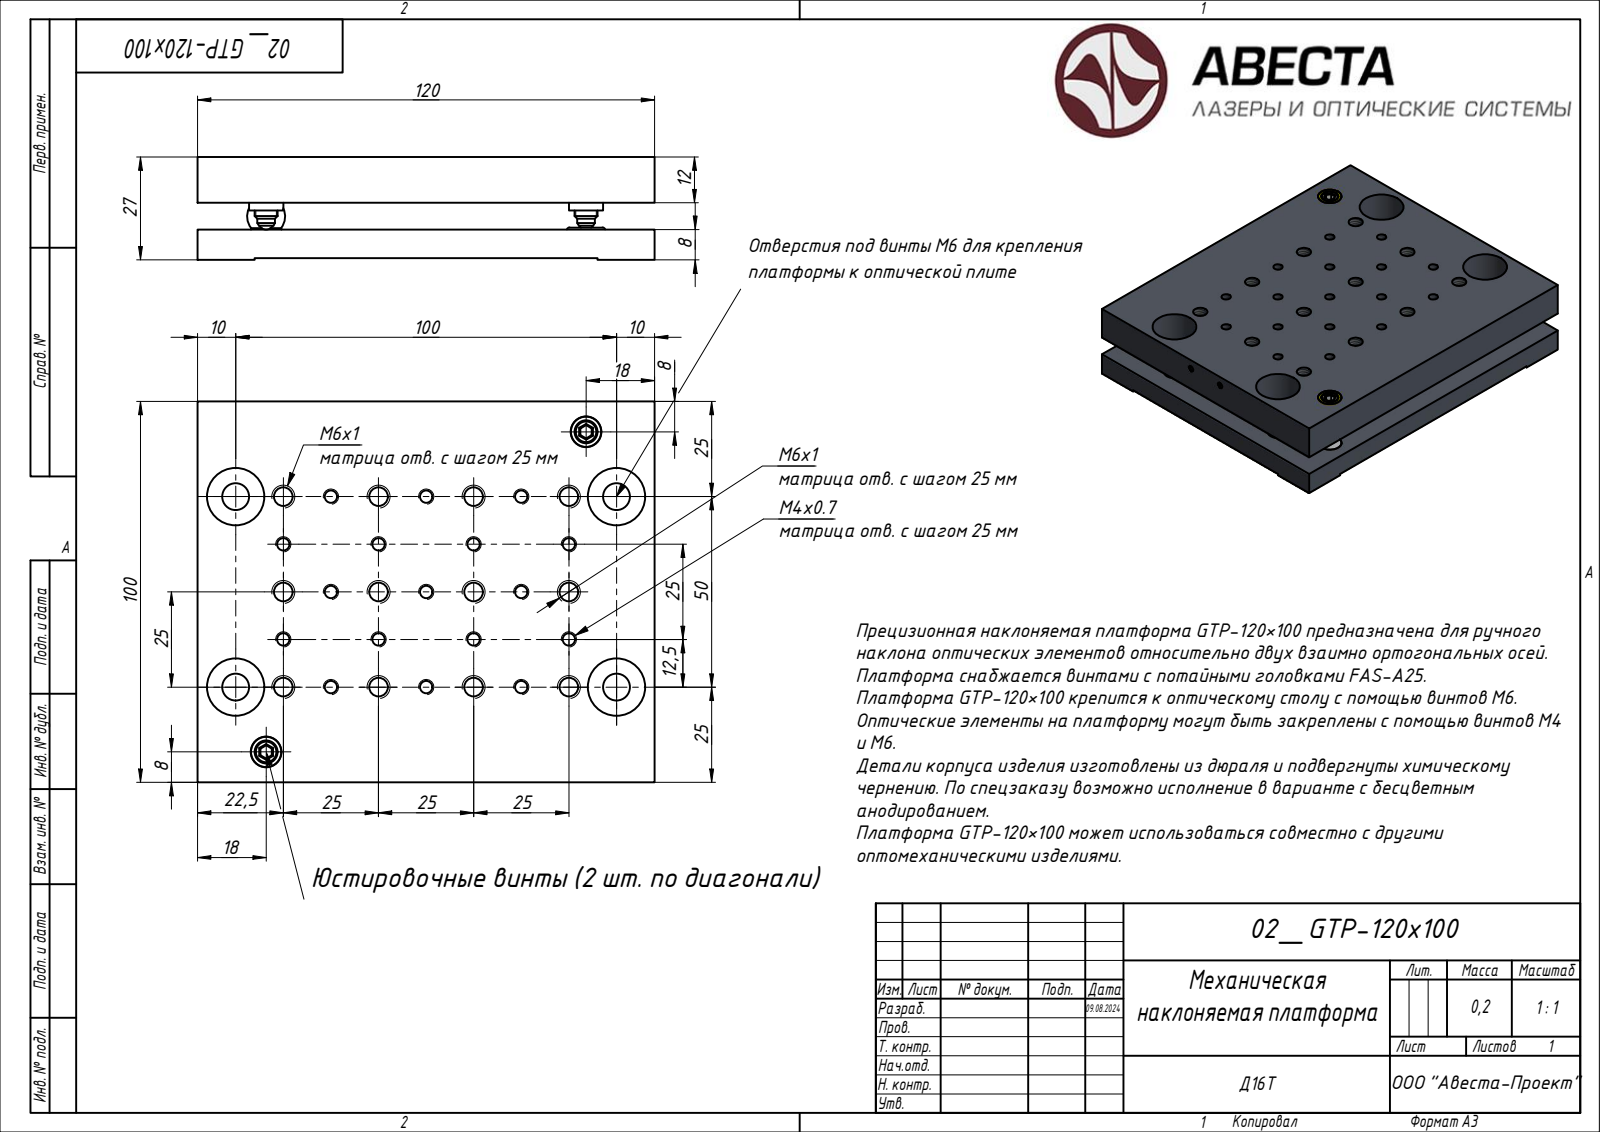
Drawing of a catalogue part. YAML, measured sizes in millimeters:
step_written_by: "ST-DEVELOPER v15 (AUTOMOTIVE_DESIGN)"
units: millimeters
bodies: {solids: 20, faces: 367, planar: 0, cylindrical: 0, other: 367}
overall_size: [120, 100, 27]
volume: 218536
surface_area: 67973
